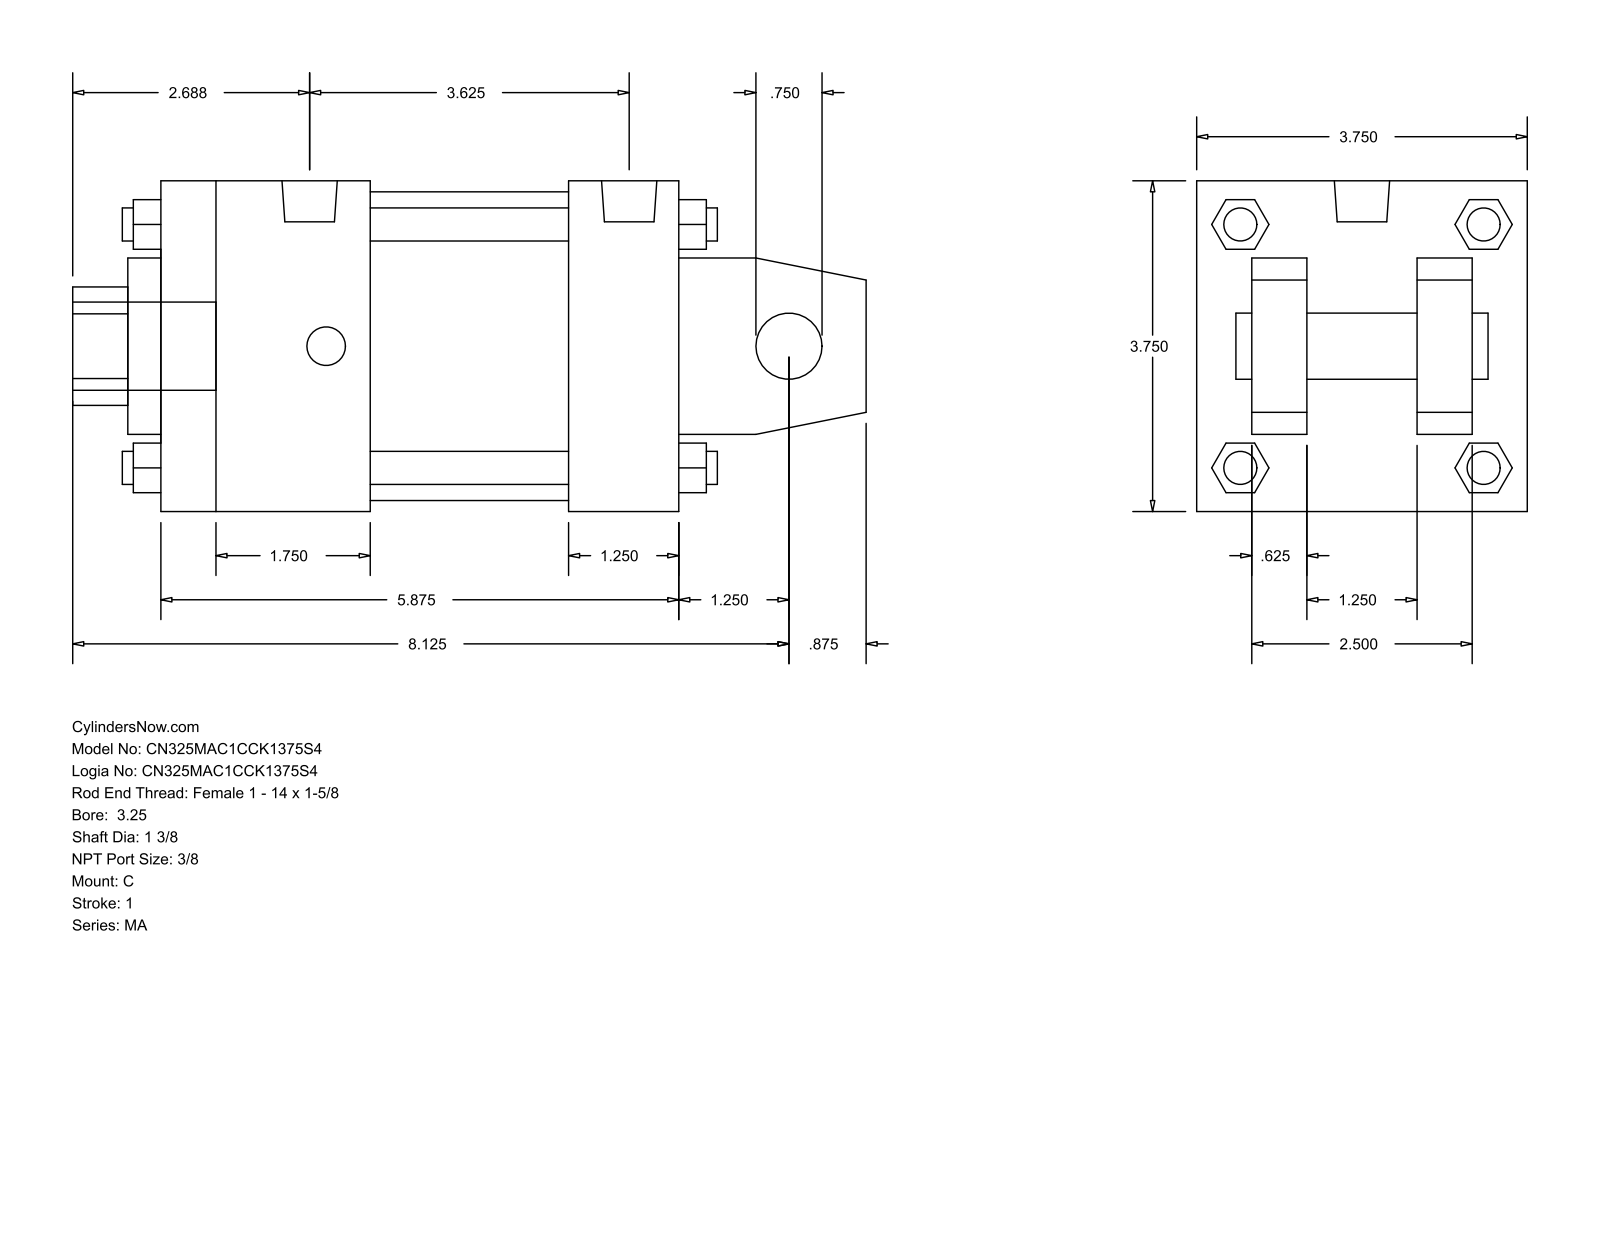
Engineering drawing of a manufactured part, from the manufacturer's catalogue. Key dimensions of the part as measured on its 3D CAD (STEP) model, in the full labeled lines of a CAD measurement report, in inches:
Part name (STEP PRODUCT): MA_C__0325_1.375
STEP written by: GSSL Pune (CONFIG_CONTROL_DESIGN)
Units: inches
Bodies: 0 solids, 139 faces (108 planar, 31 cylindrical, 0 other)
Overall size (bounding box): 9 × 3.75 × 3.75
Round holes (diameter × count): ⌀0.75 ×1, ⌀1.375 ×1, ⌀2 ×1, ⌀3.5 ×1
Round bosses / shafts (diameter × count): ⌀0.437 ×4, ⌀0.375 ×4, ⌀0.627 ×2, ⌀1 ×1
Partial cylindrical surfaces — rounded edges, fillets, slot ends (radius × count): R0.672 ×1
Main face-to-face distances: 3.75, 0.625, 1.25, 2.5, 5.875, 3.125, 1.875, 4.625, 2.375, 2.25
